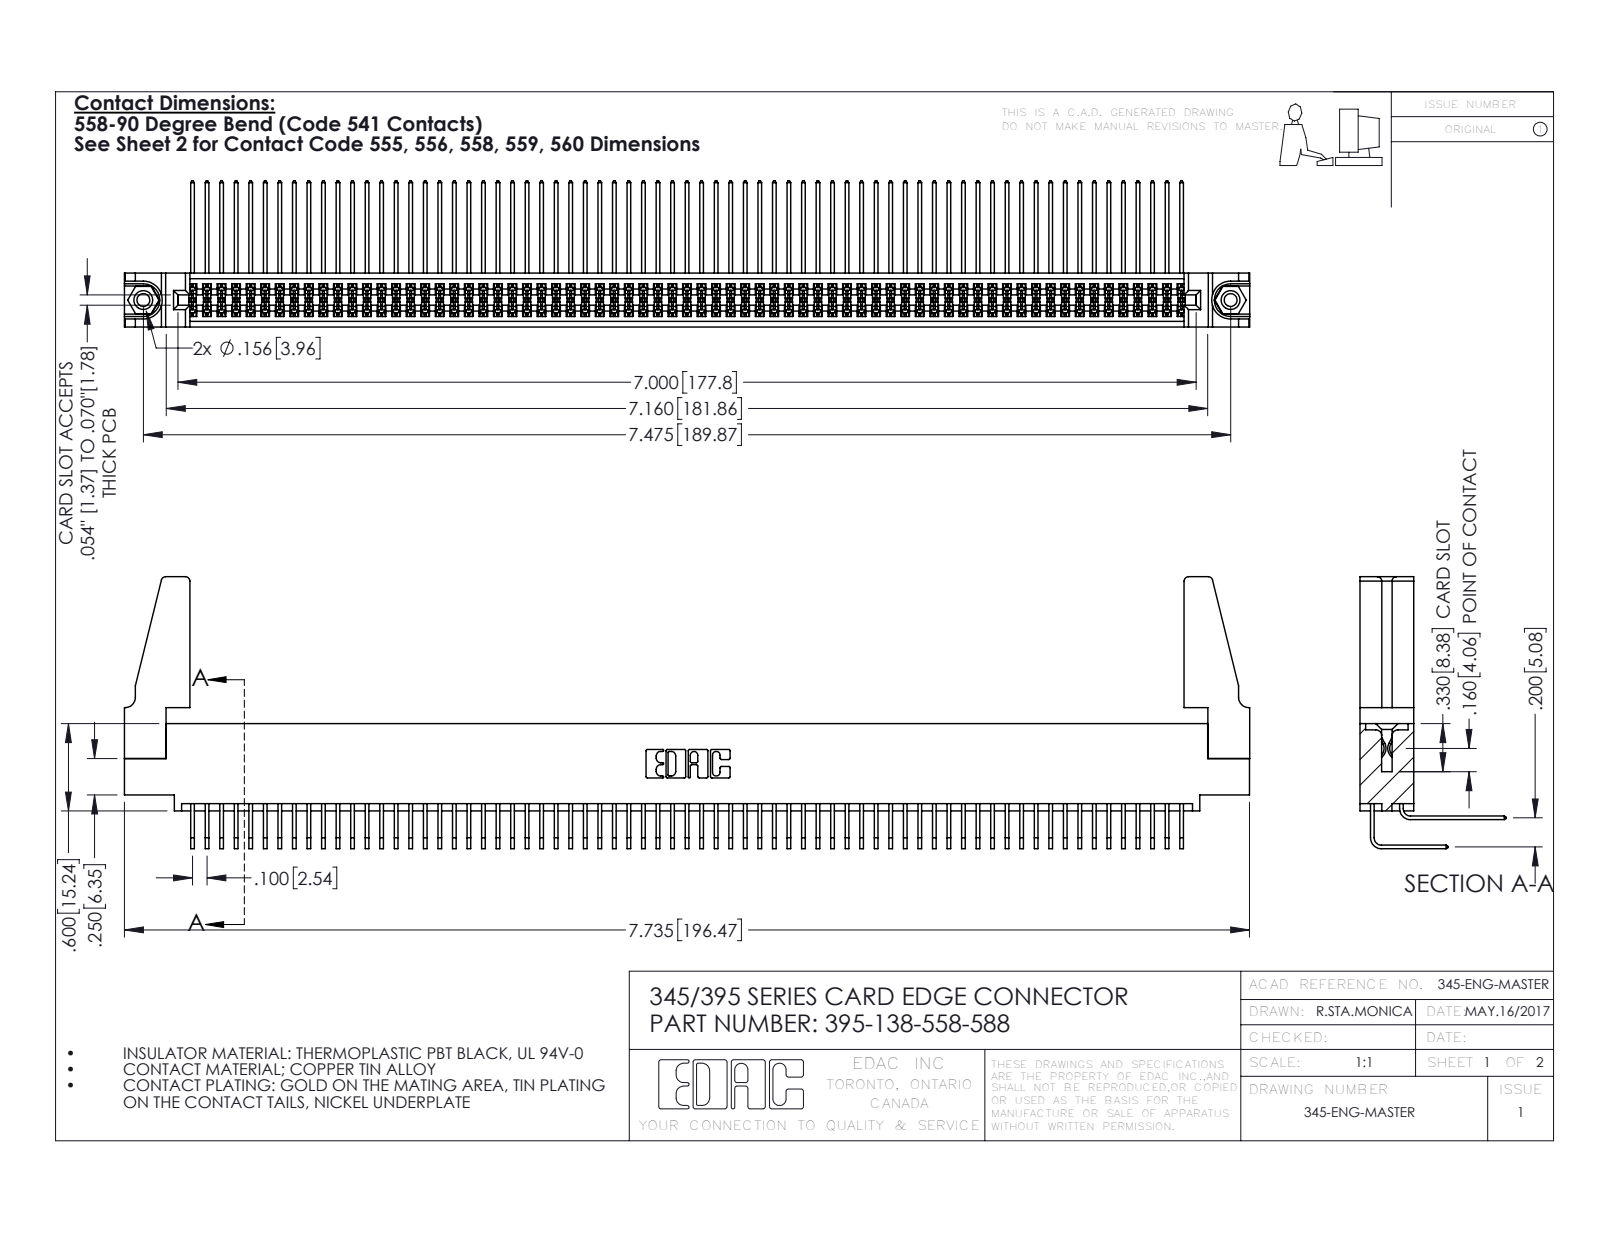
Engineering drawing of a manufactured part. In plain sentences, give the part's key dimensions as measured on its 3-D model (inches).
The part is named "345-292-001_558 Tail - 2; 345 Part_0.110 Offset - 0.156 Dia-TH; 345-292-001_558 559 Tail - 1; 345-220-078_345-220-088 (+2 more)". Its 3-D file was written by "SolidWorks 2016 (CONFIG_CONTROL_DESIGN)". It is 143 solids with 7430 faces: 4986 planar, 2428 cylindrical and 16 other. Overall it measures 7.736 by 1.869 by 1.005 inches. Its volume is 1.423 cubic inches and its surface area 57.56 square inches. Round holes: 2 of diameter 0.089, 2 of diameter 0.125, 2 of diameter 0.156, 1 of diameter 0.064. Round bosses or shafts: 2 of diameter 0.155. Partial cylindrical surfaces (rounded edges, fillets, slot ends): 275 of radius 0.006, 22 of radius 0.01, 8 of radius 0.03, 6 of radius 0.007, 6 of radius 0.031, 3 of radius 0.026, 2 of radius 0.014, 2 of radius 0.019. The main face-to-face distances are 0.072, 0.298, 0.2, 0.37, 0.098, 0.272, 0.025, 0.225, 0.025, 0.175. The hole center spacings are 0.27, 7.239, 7.475.
